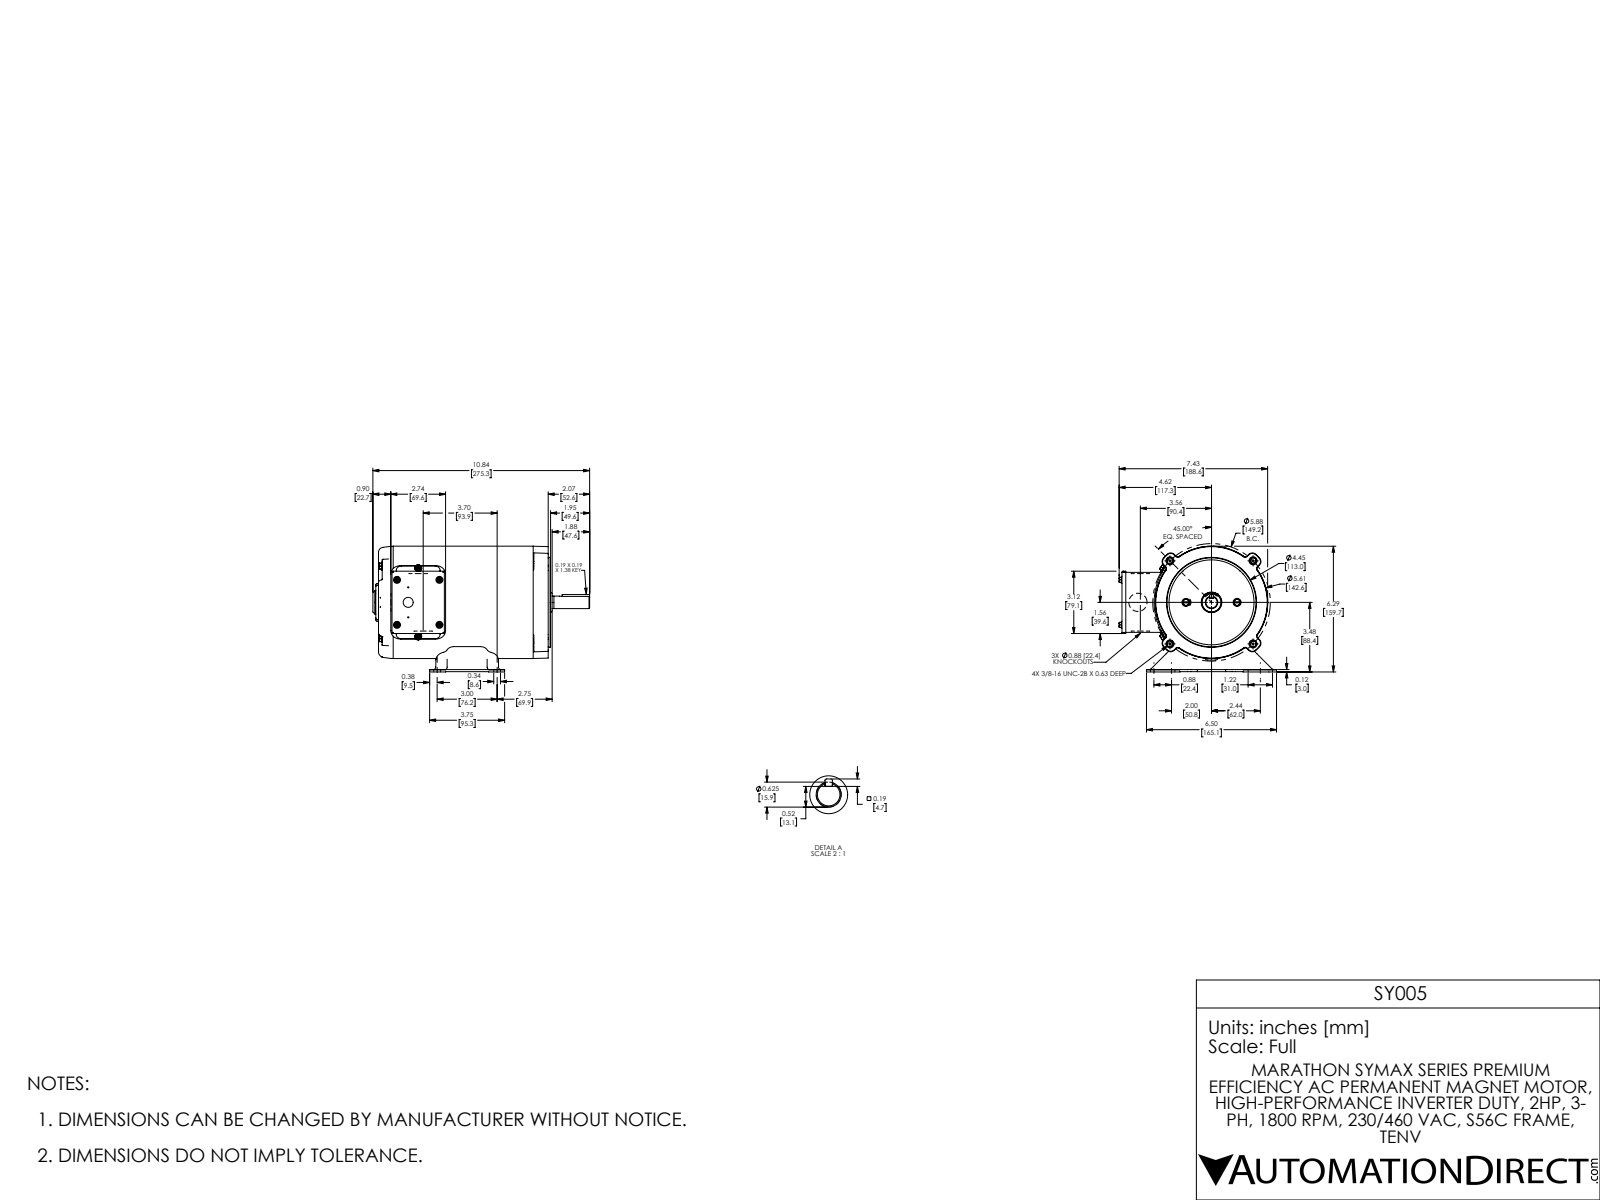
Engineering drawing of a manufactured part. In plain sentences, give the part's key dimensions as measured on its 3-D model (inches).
The part is named "614-0004-005_RevE_56C_2HP r1 Coord". Its 3-D file was written by "SolidWorks 2017 (AUTOMOTIVE_DESIGN)". It is 25 solids with 5325 faces: 2945 planar, 586 cylindrical and 1794 other. Overall it measures 10.837 by 7.869 by 6.29 inches. Its volume is 34.33 cubic inches and its surface area 658.8 square inches. Round holes: 6 of diameter 0.22, 5 of diameter 0.19, 4 of diameter 0.06, 4 of diameter 0.136, 4 of diameter 0.201, 4 of diameter 0.25, 3 of diameter 0.88, 2 of diameter 0.154, 2 of diameter 0.226, 2 of diameter 0.28, 1 of diameter 0.5, 1 of diameter 0.67. Round bosses or shafts: 6 of diameter 0.399, 6 of diameter 0.348, 6 of diameter 0.19, 6 of diameter 0.164, 4 of diameter 0.166, 3 of diameter 0.91, 1 of diameter 5.62, 1 of diameter 5.497. Partial cylindrical surfaces (rounded edges, fillets, slot ends): 54 of radius 0.06, 40 of radius 0.045, 32 of radius 0.03, 22 of radius 0.13, 18 of radius 0.17, 14 of radius 0.25, 12 of radius 0.16, 12 of radius 0.38. The main face-to-face distances are 0.048, 0.09, 8.485, 8.395, 0.104, 2.452, 0.015, 2.952, 7.75, 0.13. The hole center spacings are 2.12, 3.091, 1.893, 2.25, 2.562, 3.624, 4.548, 0.75.
